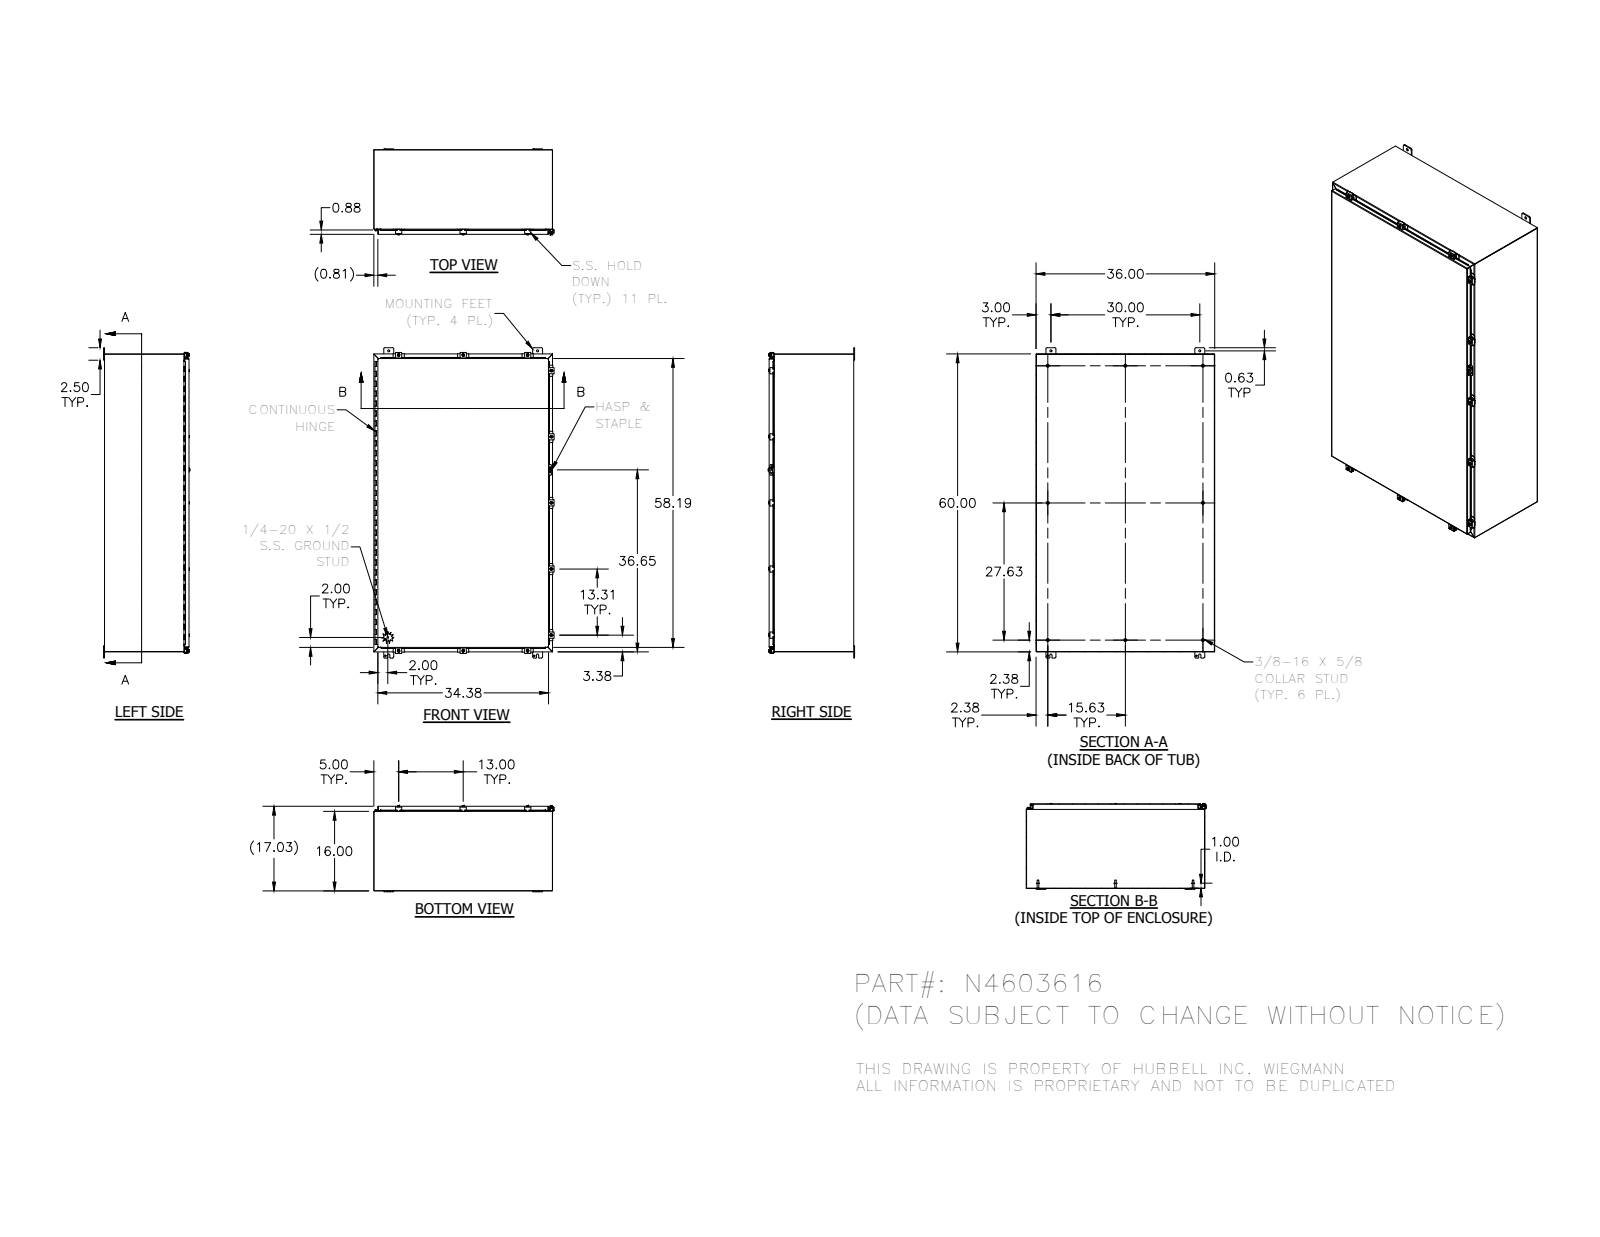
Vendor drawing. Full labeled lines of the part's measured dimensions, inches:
Part name (STEP PRODUCT): 328116_1; 30824-1_1; 328116P_1; HFW30825-3_1 (+8 more)
STEP written by: SolidWorks 2014 (AUTOMOTIVE_DESIGN)
Units: inches
Bodies: 78 solids, 3016 faces (1234 planar, 1323 cylindrical, 459 other)
Overall size (bounding box): 62.5 × 36.311 × 17.41
Volume: 614.8 in³ · Surface area: 16 346 in²
Round holes (diameter × count): ⌀0.211 ×11, ⌀0.281 ×11, ⌀0.3 ×11, ⌀0.313 ×4, ⌀0.438 ×4, ⌀0.11 ×3, ⌀0.125 ×1, ⌀0.156 ×1, ⌀0.5 ×1
Round bosses / shafts (diameter × count): ⌀0.25 ×13, ⌀0.52 ×11, ⌀0.5 ×11, ⌀0.35 ×11, ⌀0.625 ×8, ⌀0.33 ×8, ⌀0.337 ×1, ⌀0.12 ×1
Partial cylindrical surfaces — rounded edges, fillets, slot ends (radius × count): R0.03 ×129, R0.125 ×43, R0.25 ×39, R0.062 ×24, R0.141 ×22, R0.031 ×21, R0.105 ×21, R0.1 ×16
Main face-to-face distances: 0.074, 16.959, 16.885, 17.033, 35.926, 59.926, 36, 35.852, 59.852, 60
Hole centre spacings: 1.593, 13, 30, 60, 61.018, 67.082, 13.313, 59.617
